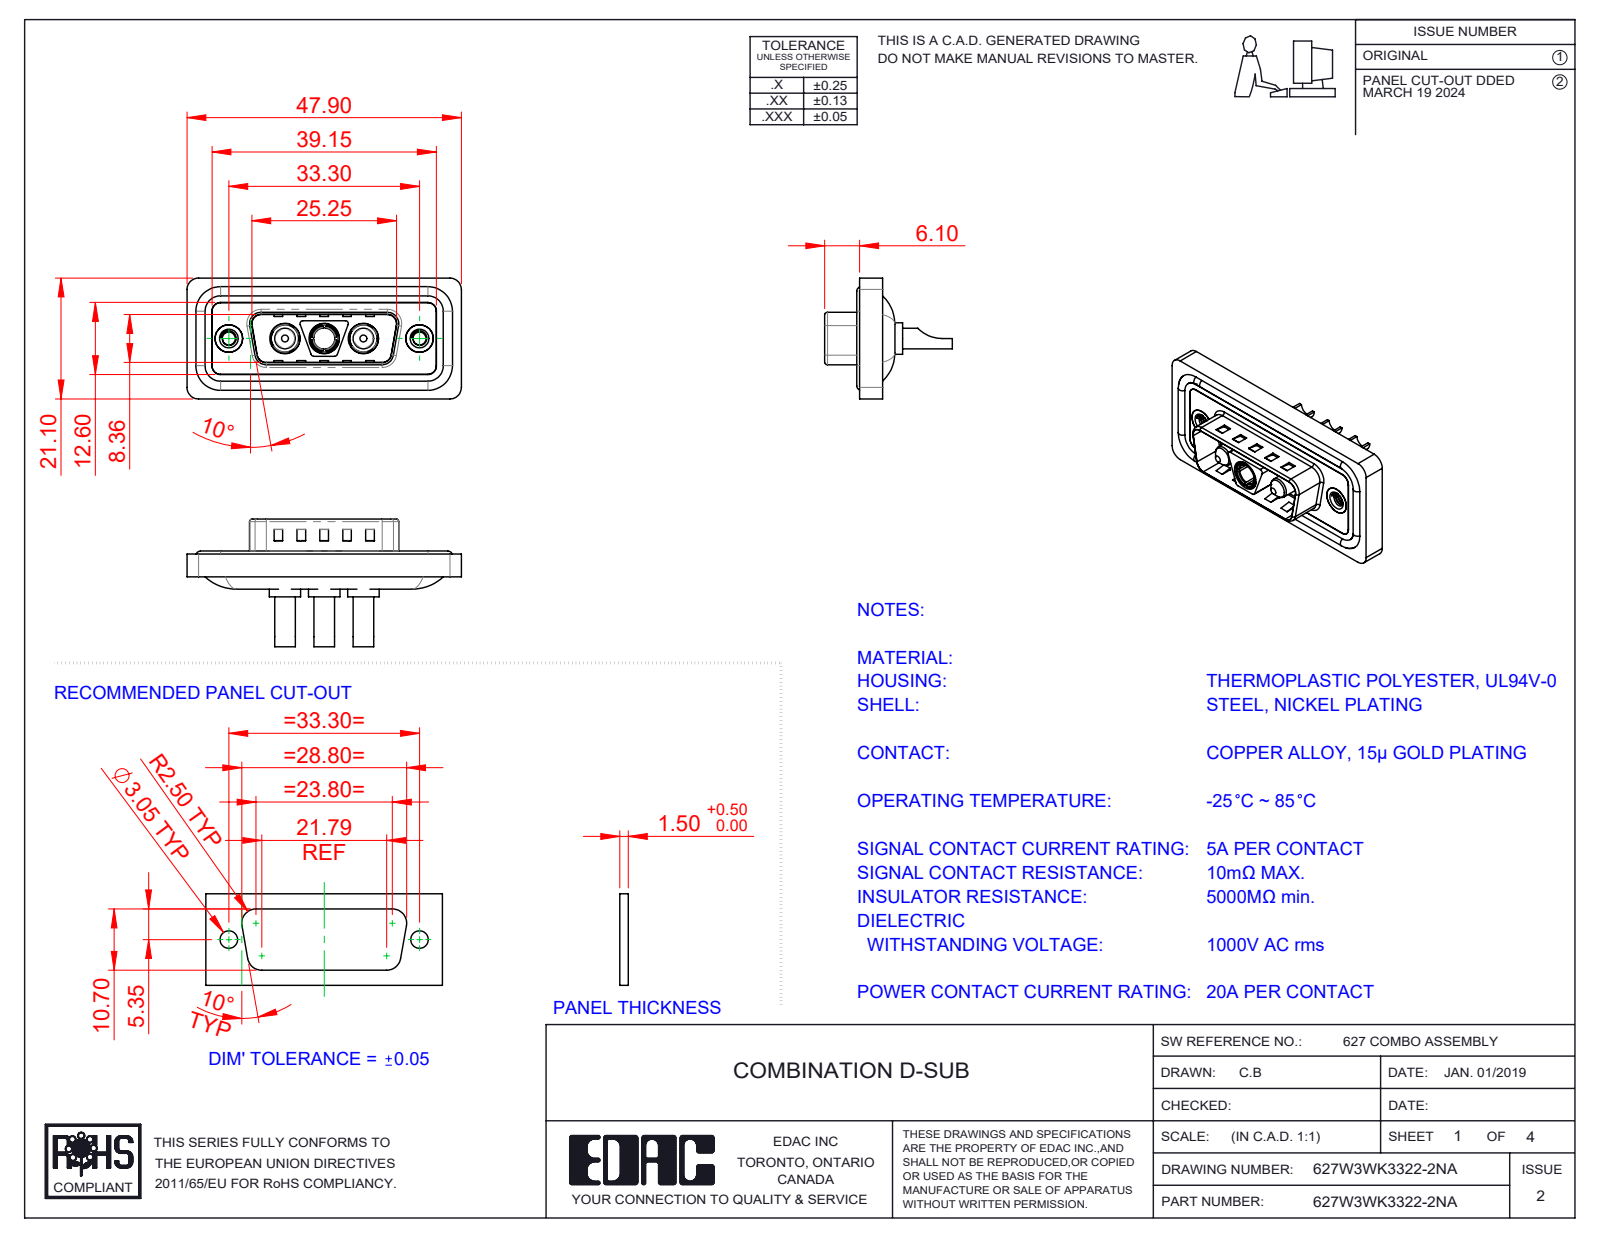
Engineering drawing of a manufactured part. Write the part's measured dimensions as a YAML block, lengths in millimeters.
part_name: "627Combo Shell Front_15 Contacts; 627Combo Housing_3WK3; Power Socket_20A SC; 627Combo Threaded Rivet_A (+4 more)"
step_written_by: "SolidWorks 2023 (CONFIG_CONTROL_DESIGN)"
units: millimeters
bodies: {solids: 13, faces: 628, planar: 240, cylindrical: 261, other: 127}
overall_size: [47.9, 22.3, 21.1]
volume: 5728
surface_area: 9372
round_holes:
  - {diameter: 2.7, count: 3}
  - {diameter: 4.85, count: 3}
  - {diameter: 5.3, count: 3}
  - {diameter: 2.26, count: 2}
  - {diameter: 4, count: 2}
  - {diameter: 4.8, count: 2}
  - {diameter: 5, count: 2}
  - {diameter: 3.7, count: 1}
round_bosses_or_shafts:
  - {diameter: 1.6, count: 4}
  - {diameter: 5.5, count: 3}
  - {diameter: 5.2, count: 3}
  - {diameter: 4.75, count: 3}
  - {diameter: 3.75, count: 3}
  - {diameter: 3.6, count: 3}
  - {diameter: 4.9, count: 2}
  - {diameter: 4.96, count: 1}
partial_cylinders:
  - {radius: 1.5, count: 26}
  - {radius: 2, count: 20}
  - {radius: 0.5, count: 12}
  - {radius: 1.6, count: 8}
  - {radius: 0.25, count: 4}
  - {radius: 0.6, count: 4}
  - {radius: 0.65, count: 4}
  - {radius: 0.9, count: 4}
face_to_face_distances: [0.4, 1.1, 0.5, 1.5, 1.6, 3.1, 2.9, 4, 0.82, 9.58]
hole_center_spacings: [6.85, 9.8, 16.65, 23.5, 13.7, 33.3]
